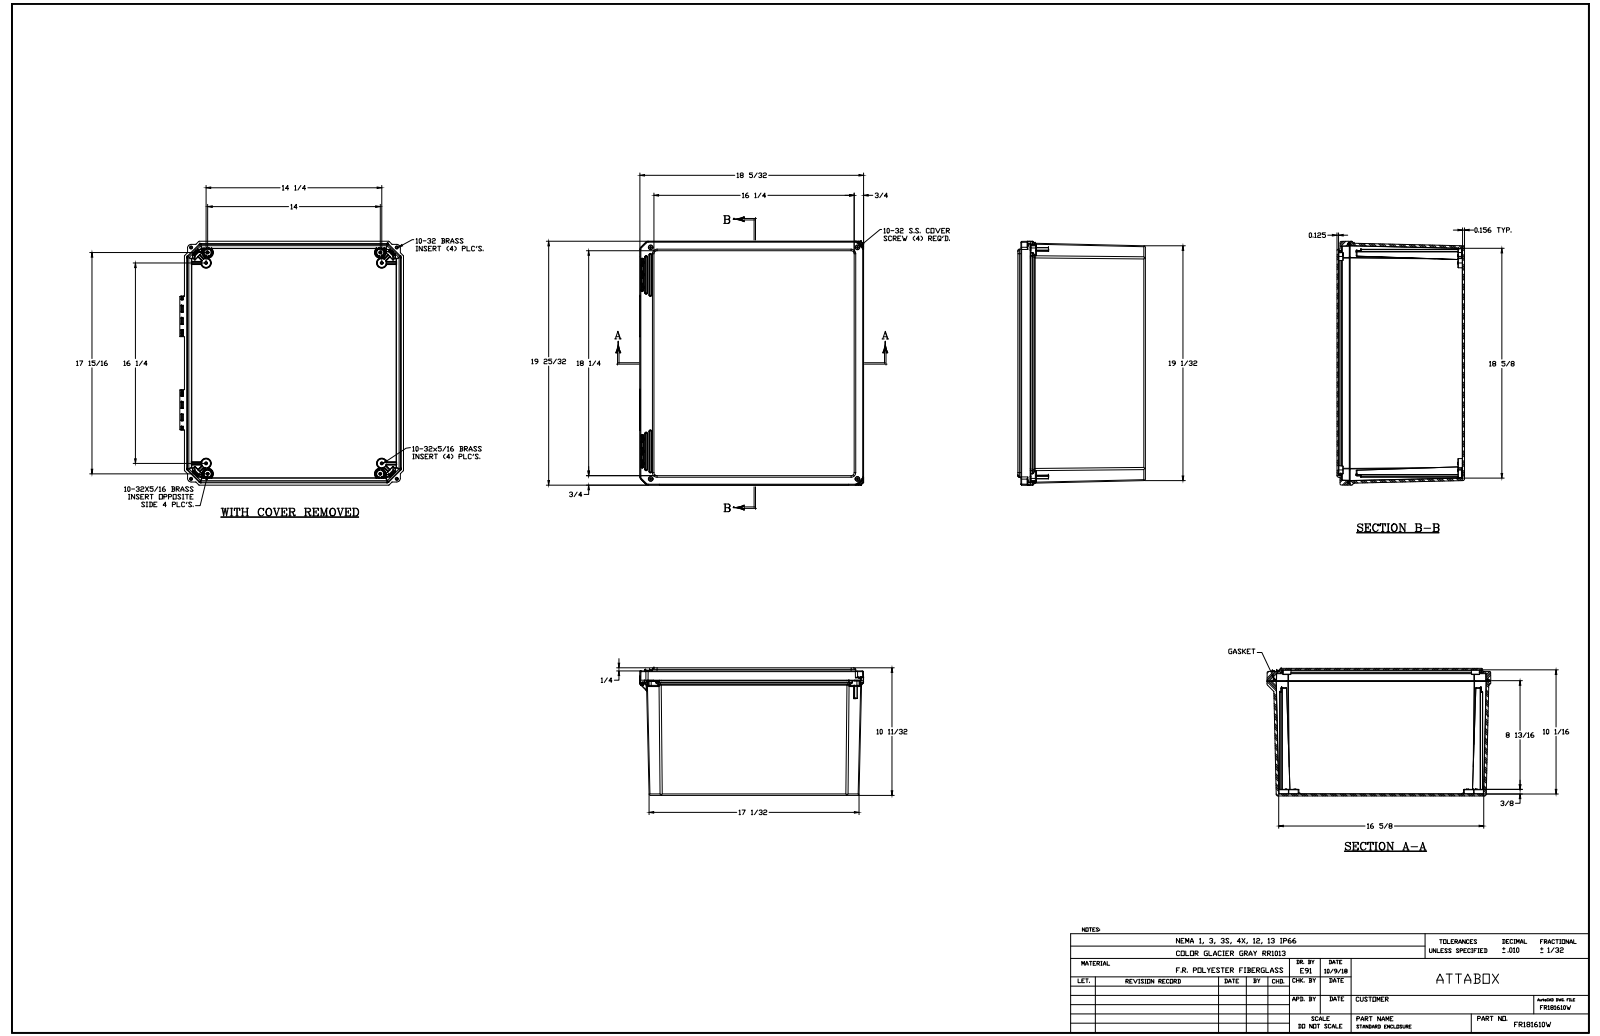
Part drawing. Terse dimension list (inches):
name: FR181610W
written by: SolidWorks 2018 (AUTOMOTIVE_DESIGN)
unit: in
bodies: 27 solids, 2163 faces (742 planar, 786 cylindrical, 635 other)
size: 19.788 × 18.147 × 10.341
volume: 257.2 in³; area: 2 943 in²
holes: 16× ⌀0.156, 8× ⌀0.152, 4× ⌀0.252, 4× ⌀0.253, 2× ⌀0.219, 2× ⌀0.227, 2× ⌀0.313, 1× ⌀0.137
bosses: 16× ⌀0.246, 4× ⌀0.45, 4× ⌀0.199, 2× ⌀0.435
rounds: 170× R0.01, 88× R0.005, 49× R0.02, 42× R0.03, 24× R0.03, 24× R0.09, 24× R0.096, 22× R0.125
face distances: 0.125, 0.156, 10.185, 10.341, 0.202, 0.2, 10.217, 10.061, 0.25, 0.125
hole spacings: 23.392, 14.15, 15.562, 0.856, 15.391, 17.098, 17.556, 1.446
